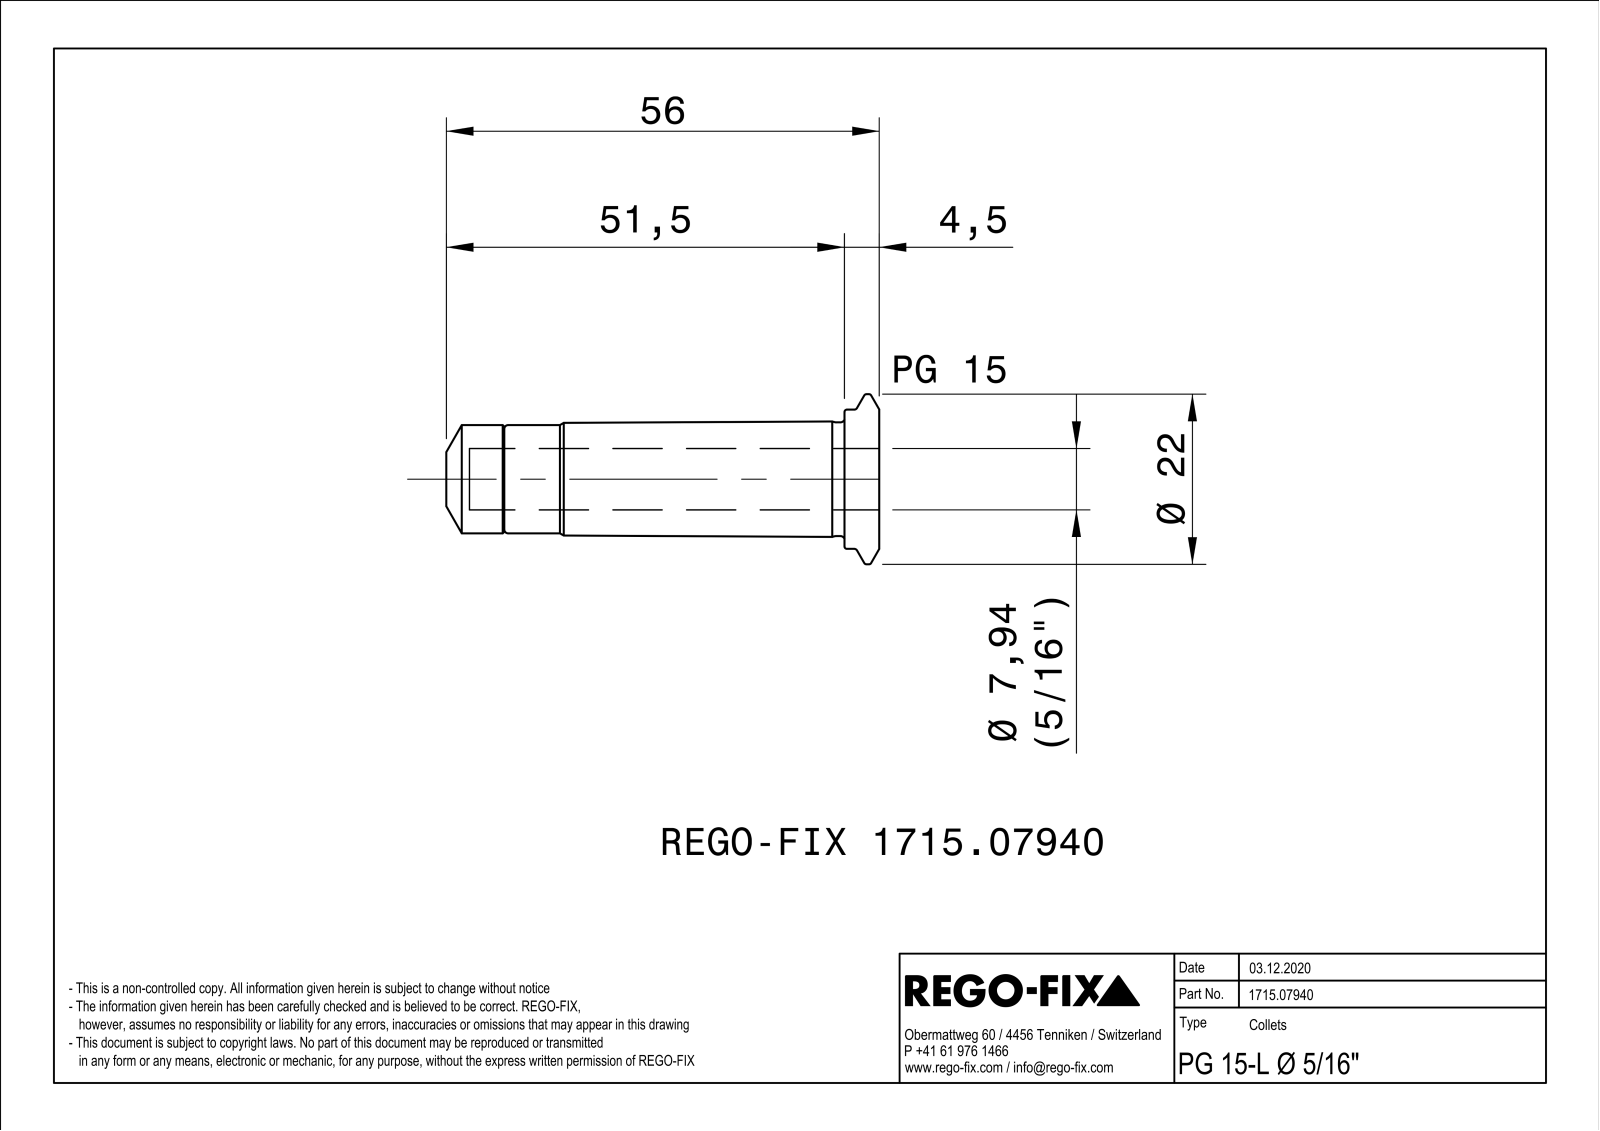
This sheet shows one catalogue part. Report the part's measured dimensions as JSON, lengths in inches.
{"part_name": "0016442", "step_written_by": "SIEMENS PLM Software Solid Edge ST10 (AUTOMOTIVE_DESIGN)", "units": "inches", "bodies": {"solids": 1, "faces": 97, "planar": 24, "cylindrical": 28, "other": 45}, "overall_size": [2.205, 0.866, 0.866], "volume_in3": 0.049, "surface_area_in2": 8.902, "round_holes": [[0.11, 1], [0.313, 1], [0.335, 1], [0.362, 1], [0.43, 1], [0.48, 1]], "round_bosses_or_shafts": [[0.866, 1], [0.709, 1], [0.579, 1], [0.551, 1], [0.472, 1], [0.409, 1]], "partial_cylinders_radius": [[0.02, 6], [0.079, 3]], "face_to_face_distances": [0.039, 1.909, 2.205, 0.295, 0.177, 1.732, 2.028, 1.685, 1.508, 0.224]}
